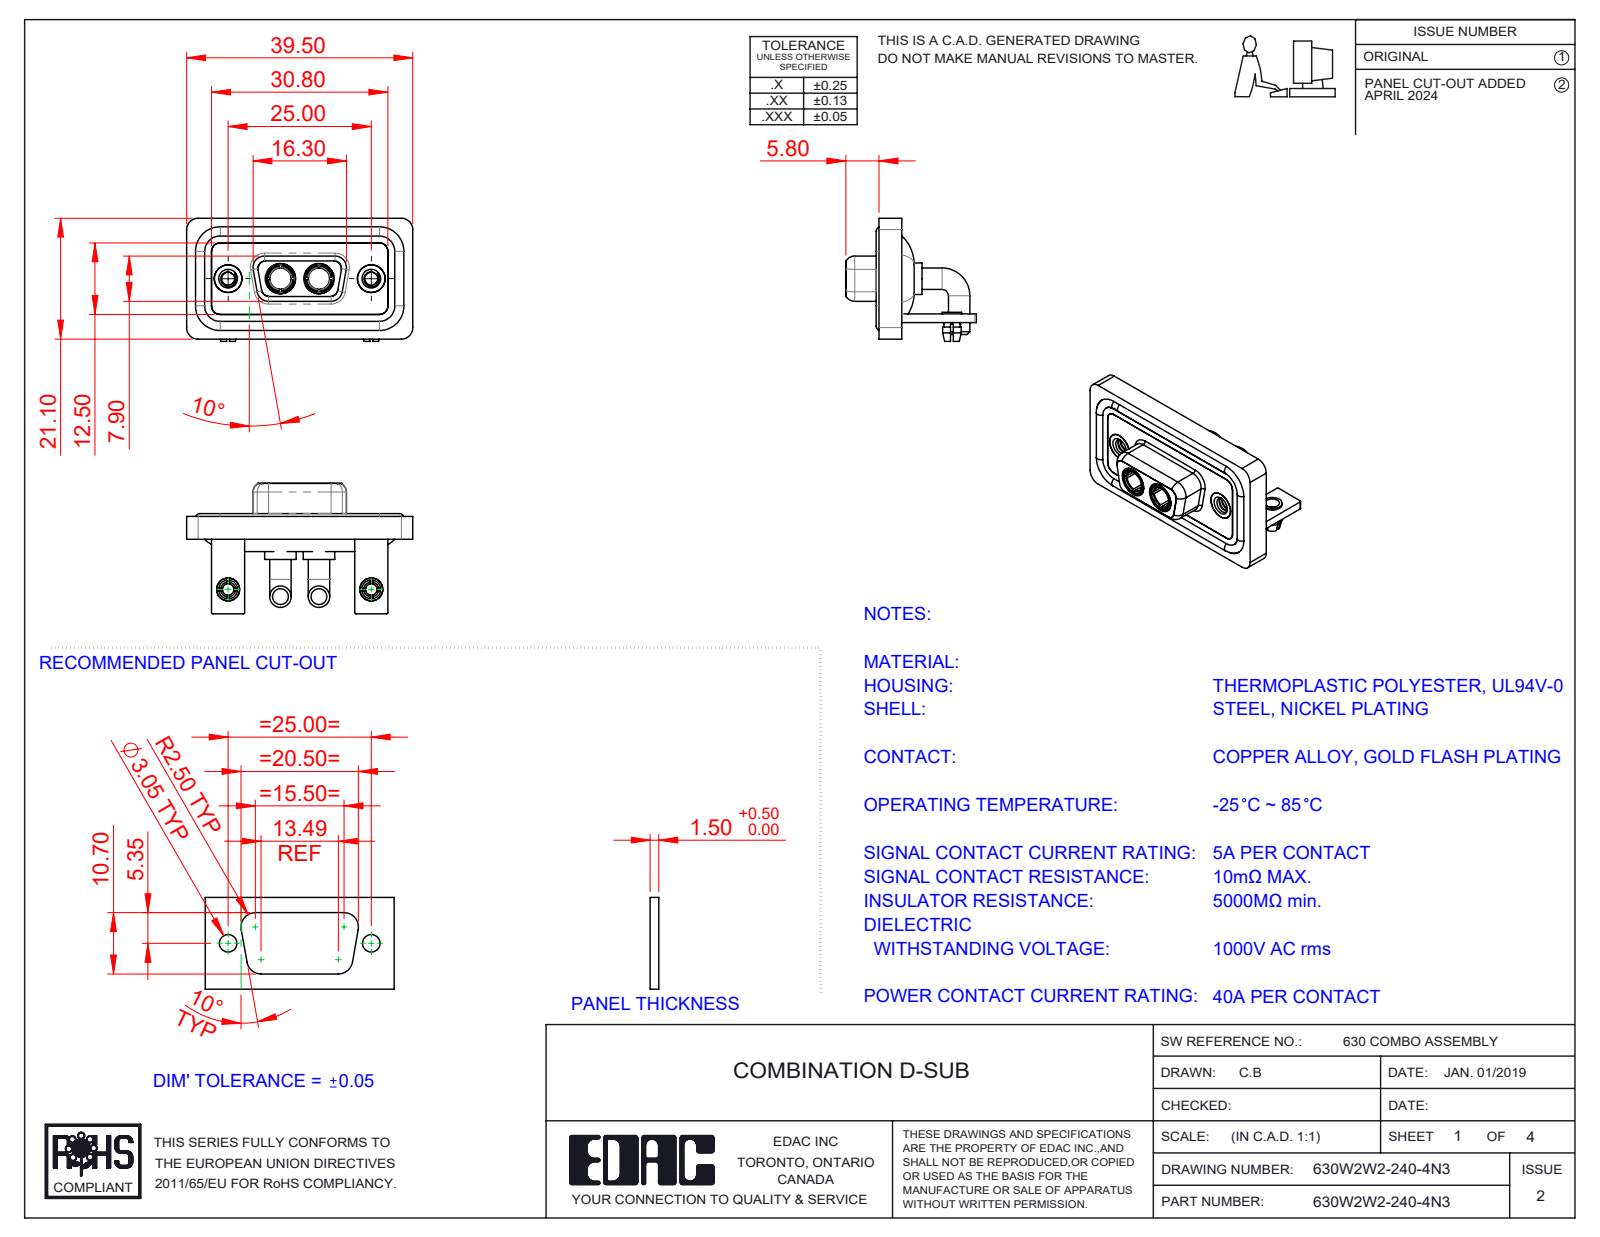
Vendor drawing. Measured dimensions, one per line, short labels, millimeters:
name: 630Combo Shell Rear_09 Contacts; 630Combo Shell Front_09 Contacts; 630Combo Threaded Rivet_2; 630Combo Board Lock_50 Contacts (+5 more)
written by: SolidWorks 2023 (CONFIG_CONTROL_DESIGN)
unit: mm
bodies: 15 solids, 682 faces (231 planar, 294 cylindrical, 157 other)
size: 39.5 × 22.8 × 21.5
volume: 5 364 mm³; area: 8 819 mm²
holes: 4× ⌀4.85, 2× ⌀2, 2× ⌀2.26, 2× ⌀2.5, 2× ⌀3.2, 2× ⌀3.7, 2× ⌀4, 2× ⌀4.05, 2× ⌀5, 2× ⌀5.3
bosses: 4× ⌀3.75, 4× ⌀1.6, 2× ⌀5.5, 2× ⌀5.2, 2× ⌀4.96, 2× ⌀4.95, 2× ⌀4.8, 2× ⌀4.75
rounds: 19× R2, 18× R1.5, 16× R0.25, 8× R1.35, 8× R1.6, 5× R0.5, 4× R0.6, 4× R0.65
face distances: 0.4, 2.9, 1.5, 1.8, 1.1, 3.7, 0.8, 2.5, 1.6, 3.1
hole spacings: 9.14, 15.86, 25, 6.72
